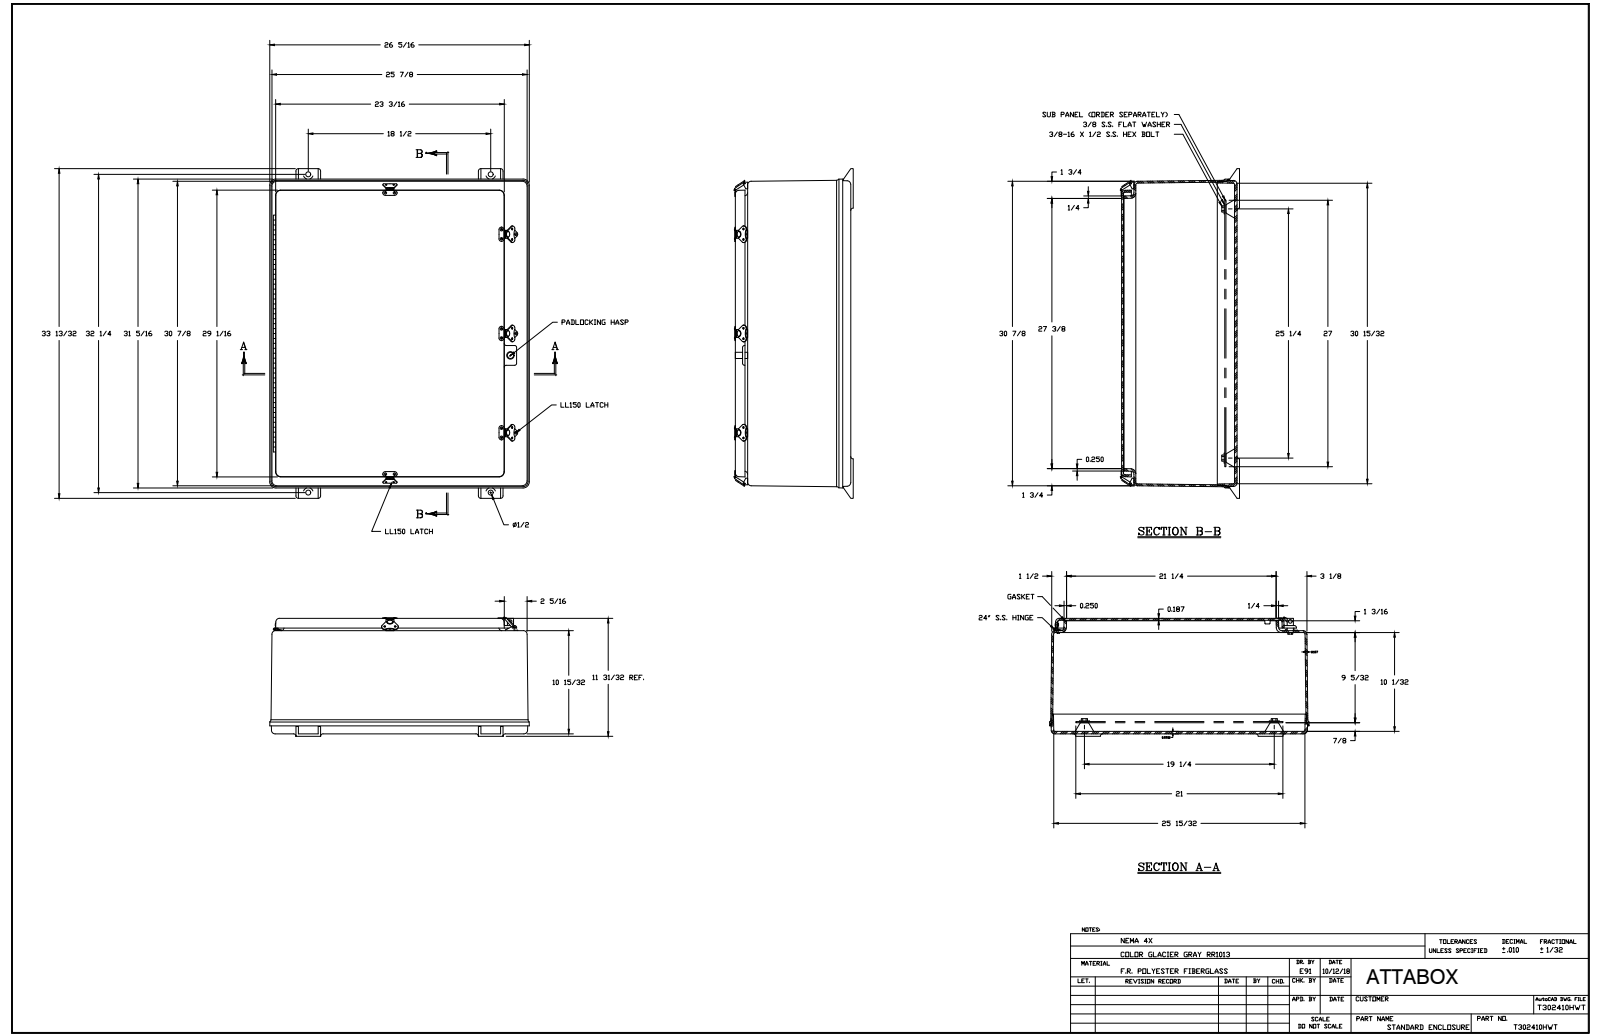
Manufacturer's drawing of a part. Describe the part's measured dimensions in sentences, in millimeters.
The part is named "T302410HWT". Its 3-D file was written by "SolidWorks 2018 (AUTOMOTIVE_DESIGN)". It is 65 solids with 1791 faces: 683 planar, 710 cylindrical and 398 other. Overall it measures 848.5 by 668.4 by 311.7 millimeters. Its volume is 10 560 000 cubic millimeters and its surface area 4 243 000 square millimeters. Round holes: 32 of diameter 3.3, 20 of diameter 1.6, 10 of diameter 3.5, 10 of diameter 4.7, 8 of diameter 2.5, 8 of diameter 5.1, 4 of diameter 7.1, 4 of diameter 14.3, 3 of diameter 4, 2 of diameter 3.4, 2 of diameter 3.7, 2 of diameter 13. Round bosses or shafts: 20 of diameter 3.6, 8 of diameter 9.1, 8 of diameter 4.7, 5 of diameter 12.7, 3 of diameter 5.1, 2 of diameter 7.1, 2 of diameter 3.4, 1 of diameter 6.4. Partial cylindrical surfaces (rounded edges, fillets, slot ends): 127 of radius 0.3, 24 of radius 6.4, 20 of radius 0.8, 13 of radius 9.5, 12 of radius 4.7, 12 of radius 7.9, 12 of radius 12.7, 11 of radius 8. The main face-to-face distances are 4.7, 6.4, 4.8, 296.8, 290.5, 292.1, 285.7, 265.9, 31, 261.1. The hole center spacings are 255.6, 190.5, 511.2, 25.4, 88.6, 256.3, 393.7, 729.2.
